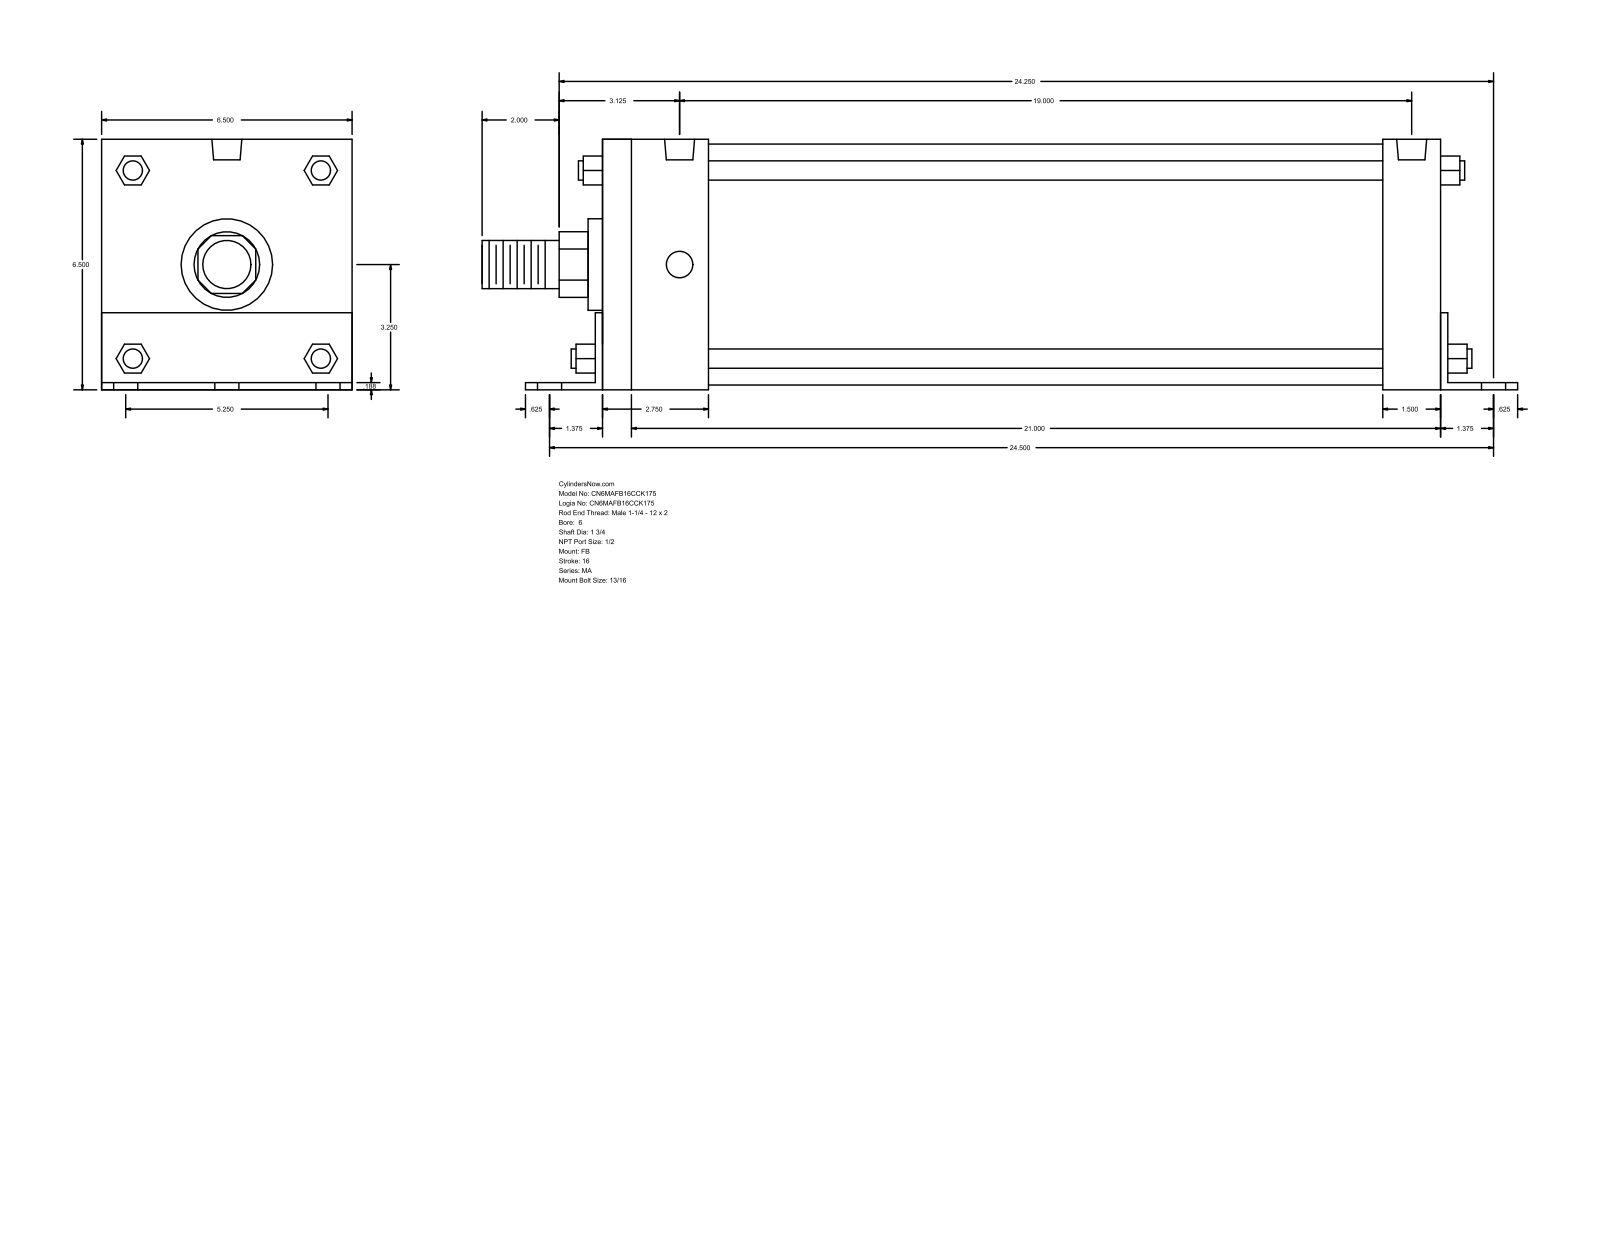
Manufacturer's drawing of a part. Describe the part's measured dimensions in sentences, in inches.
The part is named "MA_FB__0600_1.75". Its 3-D file was written by "GSSL Pune (CONFIG_CONTROL_DESIGN)". It is 0 solids with 140 faces: 105 planar, 35 cylindrical and 0 other. Overall it measures 26.875 by 6.502 by 6.5 inches. Round holes: 6 of diameter 0.813, 4 of diameter 0.687, 2 of diameter 0.778. Round bosses or shafts: 4 of diameter 0.5, 1 of diameter 6.25, 1 of diameter 2.375, 1 of diameter 1.75, 1 of diameter 1.25. Partial cylindrical surfaces (rounded edges, fillets, slot ends): 1 of radius 0.852, 1 of radius 1.262. The main face-to-face distances are 6.5, 0.187, 21.75, 6.502, 0.185, 6.315, 1.5, 2.75, 2.937, 0.188. The hole center spacings are 2.625, 24.64, 24.5, 3.377, 4.276, 5.25, 19, 21.287.
